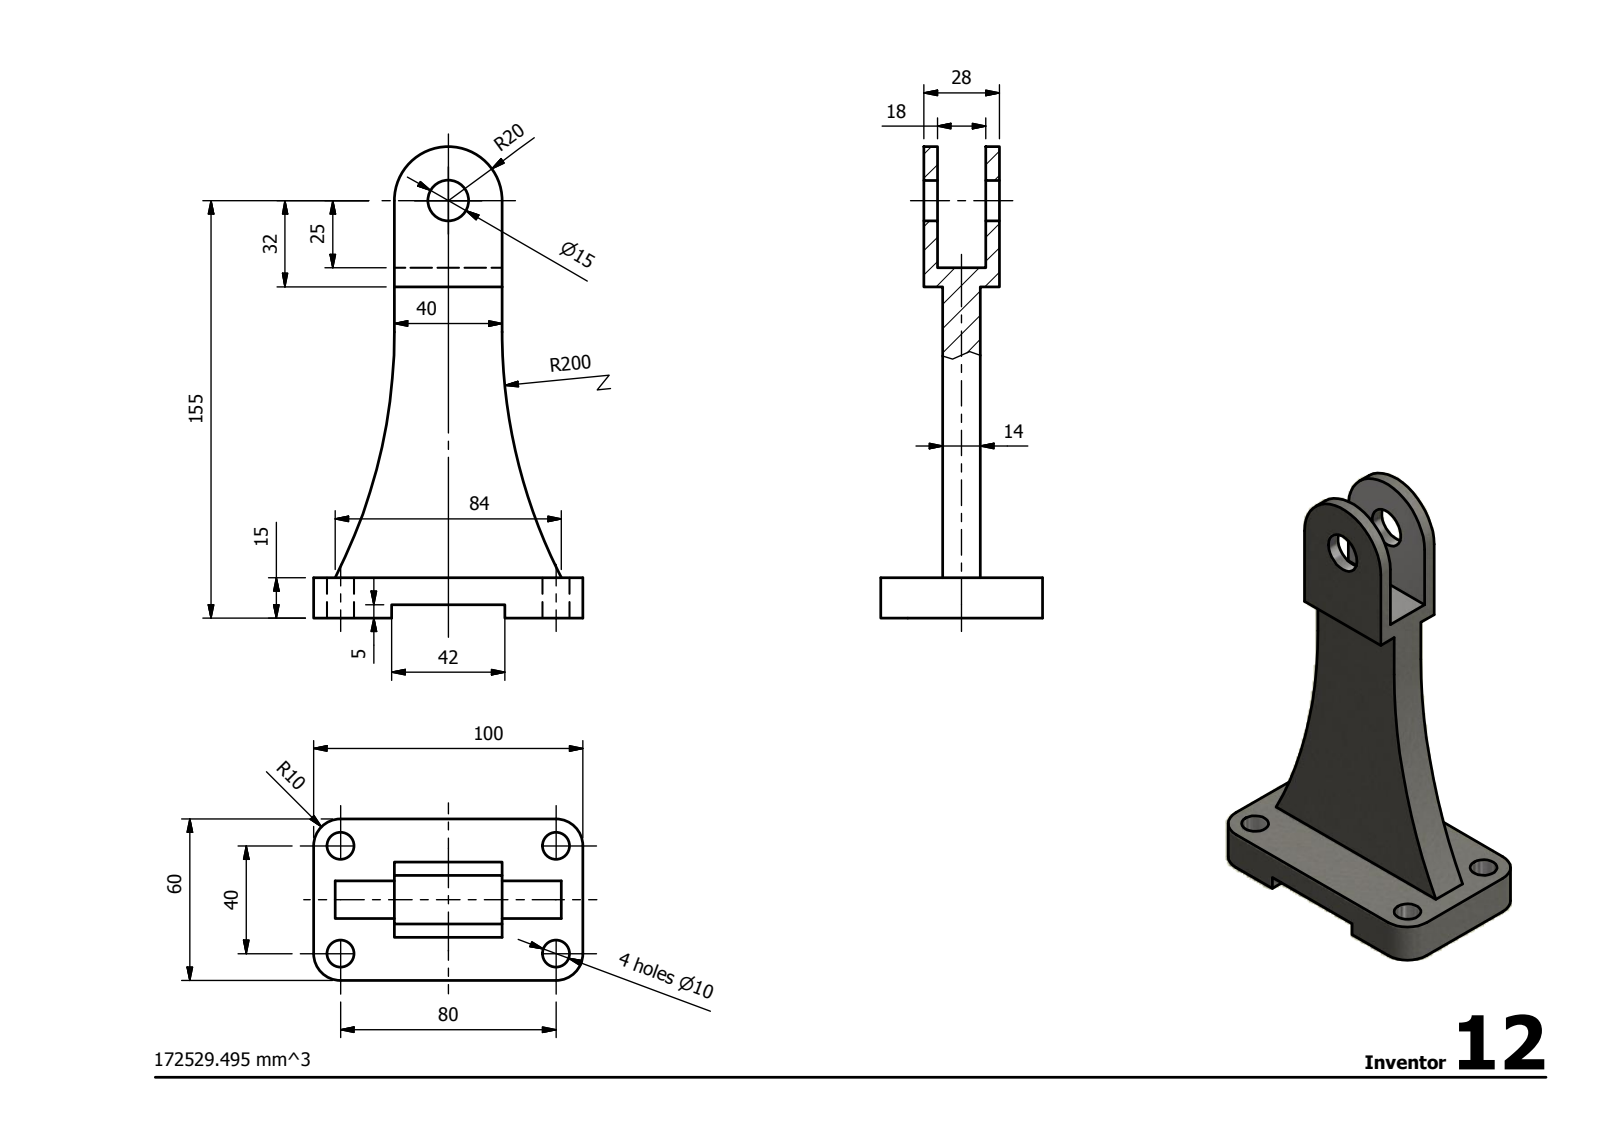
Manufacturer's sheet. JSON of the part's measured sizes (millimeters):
{"step_written_by": "Autodesk Inventor 2014 (AUTOMOTIVE_DESIGN)", "units": "millimeters", "bodies": {"solids": 1, "faces": 35, "planar": 21, "cylindrical": 14, "other": 0}, "overall_size": [175, 100, 60], "volume_mm3": 172528, "surface_area_mm2": 40645, "round_holes": [[10, 4], [15, 1]], "partial_cylinders_radius": [[10, 4], [200, 2], [20, 1]], "face_to_face_distances": [14, 21, 5, 16, 23, 7, 15, 2, 10, 37], "hole_center_spacings": [40, 80, 89.44]}
